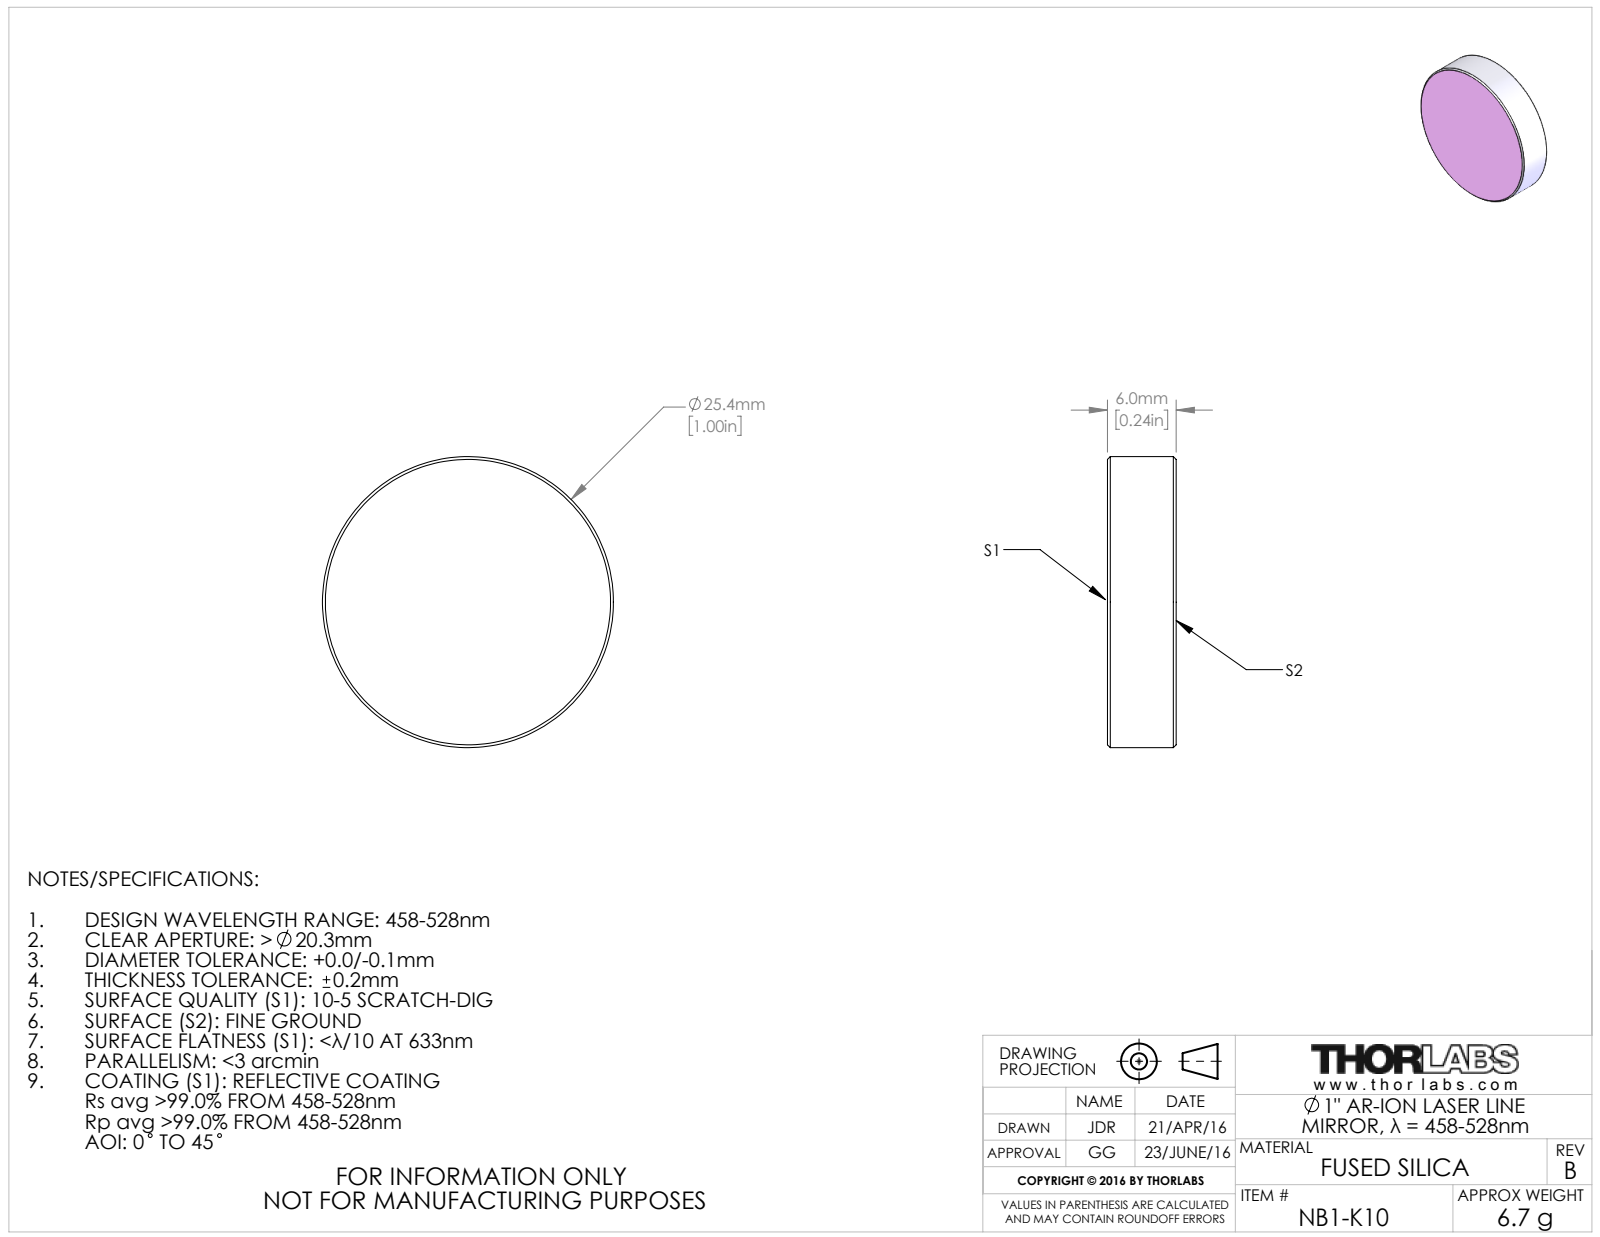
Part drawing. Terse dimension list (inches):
name: TTN050498-E0W
written by: SolidWorks 2016 (CONFIG_CONTROL_DESIGN)
unit: in
bodies: 1 solid, 31 faces (25 planar, 2 cylindrical, 4 other)
size: 1 × 1 × 0.236
volume: 0.185 in³; area: 2.276 in²
bosses: 1× ⌀1
face distances: 0.236
